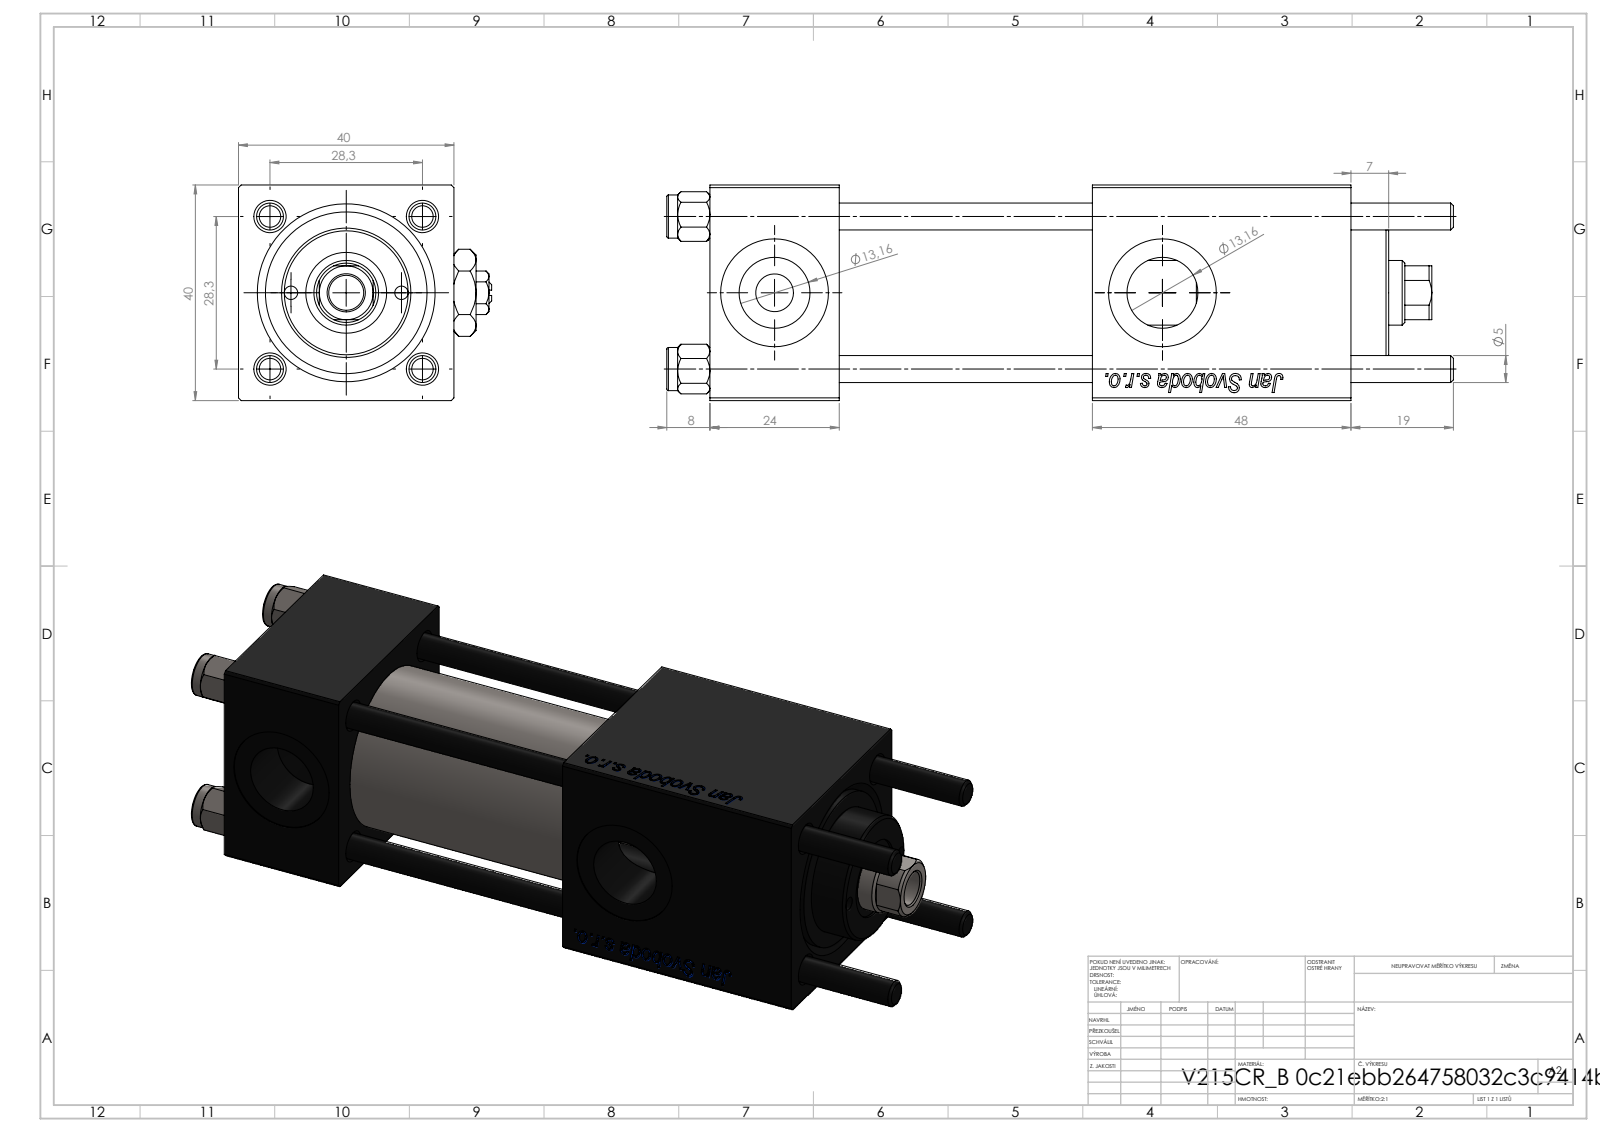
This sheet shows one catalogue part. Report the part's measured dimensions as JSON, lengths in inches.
{"part_name": "Zatka_pro_OIL_PORT; V215_VC_A; NUT_M5_B; V215CR_B_TYCINKA (+2 more)", "step_written_by": "SolidWorks 2019 (CONFIG_CONTROL_DESIGN)", "units": "inches", "bodies": {"solids": 12, "faces": 1209, "planar": 455, "cylindrical": 86, "other": 668}, "overall_size": [5.748, 1.85, 1.575], "volume_in3": 8.794, "surface_area_in2": 92.3, "round_holes": [[0.197, 4], [0.787, 3], [0.098, 2], [0.276, 2], [0.518, 2], [0.256, 1], [0.472, 1], [0.591, 1], [0.984, 1], [1.181, 1]], "round_bosses_or_shafts": [[0.315, 4], [1.22, 1], [0.945, 1]], "partial_cylinders_radius": [[0.217, 1]], "face_to_face_distances": [1.575, 0.945, 3.555, 2.61, 1.85, 2.795, 0.76, 1.89, 4.685, 3.74], "hole_center_spacings": [0.578, 0.788, 1.111, 1.114, 0.404, 1.576, 0.807, 2.835]}
